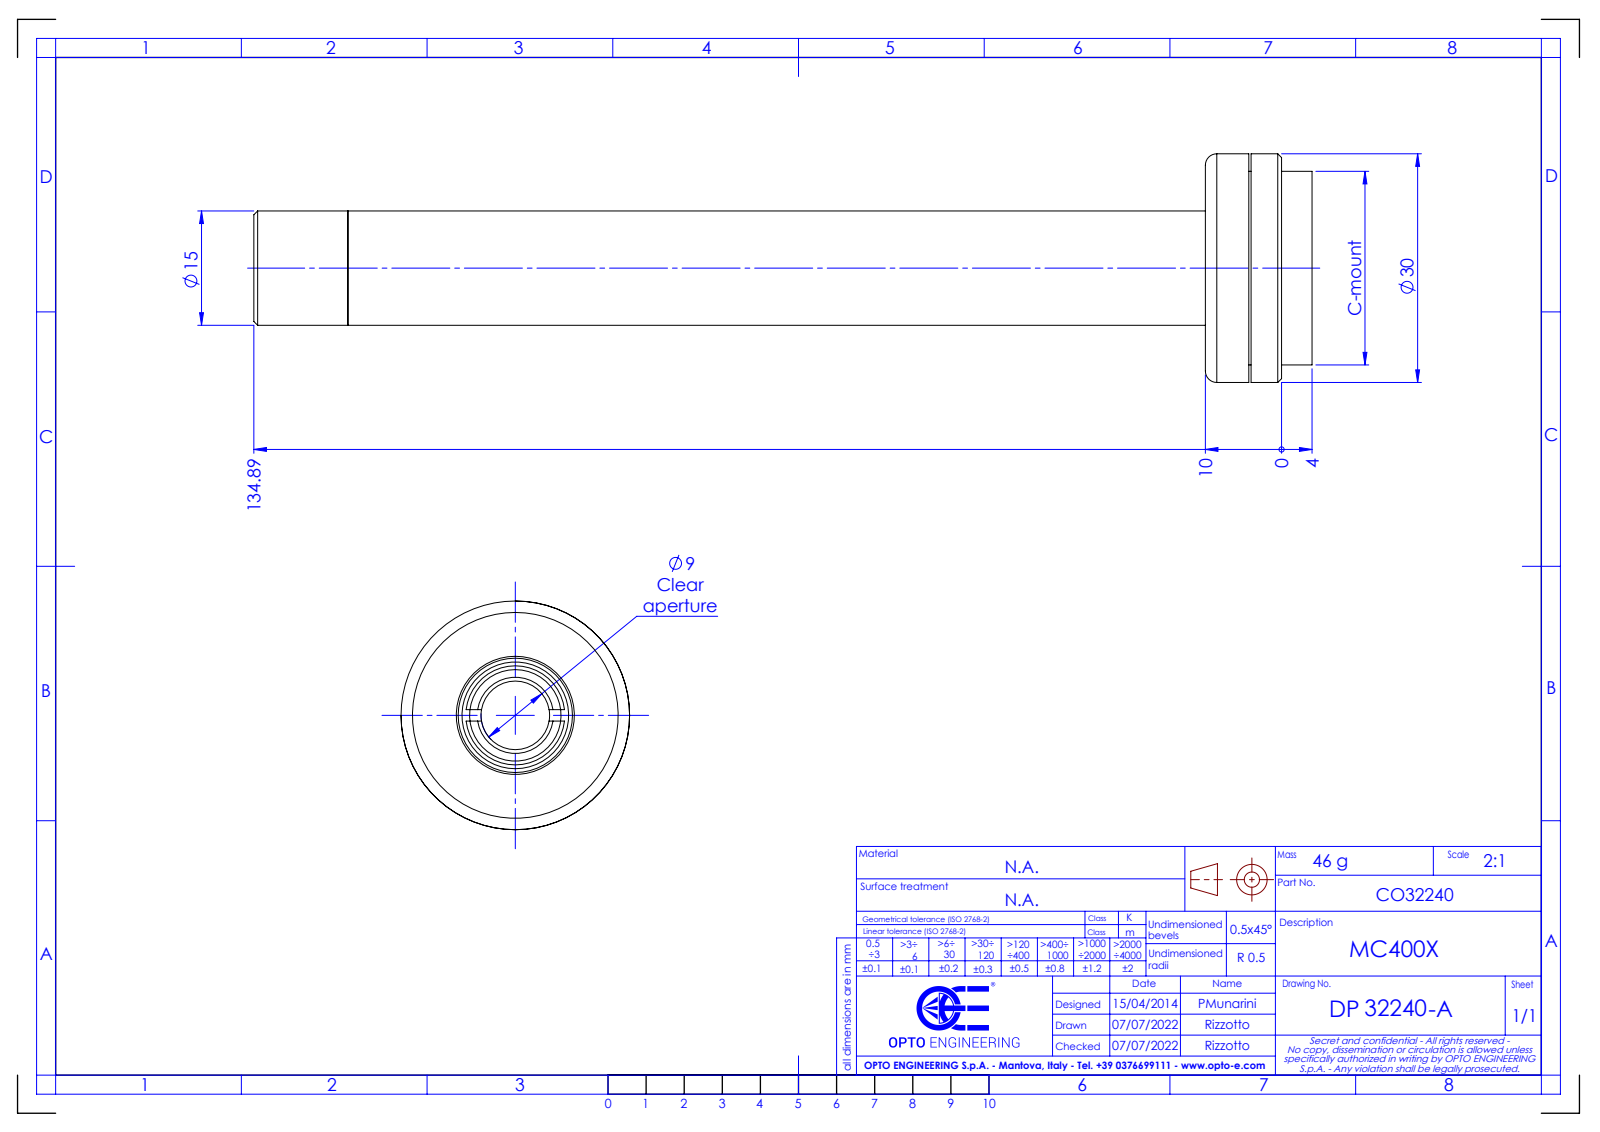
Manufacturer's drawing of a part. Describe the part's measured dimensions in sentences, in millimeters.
The part is named "DP32240-A_MC400X". Its 3-D file was written by "SolidWorks 2021 (CONFIG_CONTROL_DESIGN)". It is 0 solids with 48 faces: 15 planar, 18 cylindrical and 15 other. Overall it measures 138.89 by 30 by 30 millimeters. Round holes: 1 of diameter 9, 1 of diameter 12. Round bosses or shafts: 1 of diameter 30, 1 of diameter 25.4, 1 of diameter 15, 1 of diameter 14.5. The main face-to-face distances are 4, 6, 5.7, 10, 4.3, 14, 8.3, 8, 124.89, 130.59.
